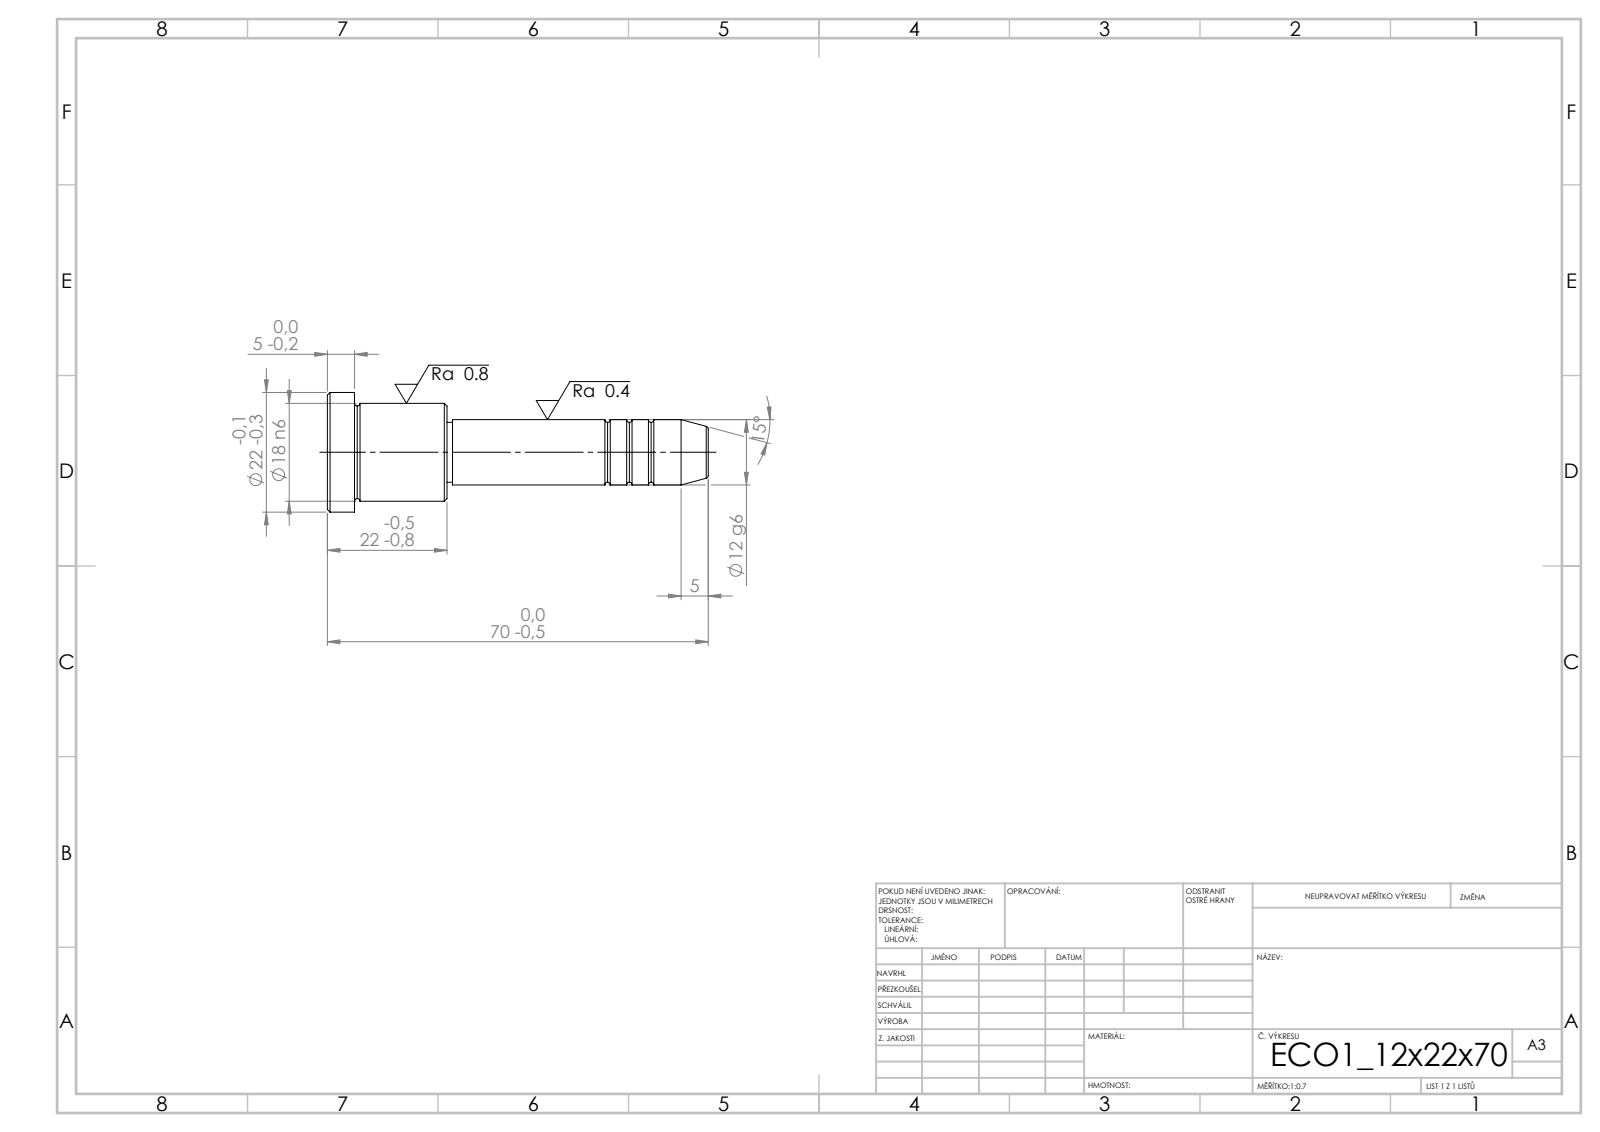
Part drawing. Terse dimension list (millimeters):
written by: SolidWorks 2019 (CONFIG_CONTROL_DESIGN)
unit: mm
bodies: 1 solid, 43 faces (5 planar, 14 cylindrical, 24 other)
size: 70 × 22 × 22
volume: 11 440 mm³; area: 3 893 mm²
bosses: 1× ⌀22, 1× ⌀18, 1× ⌀12, 1× ⌀11
face distances: 22, 17, 5, 48, 65, 70, 47, 1, 18, 23
